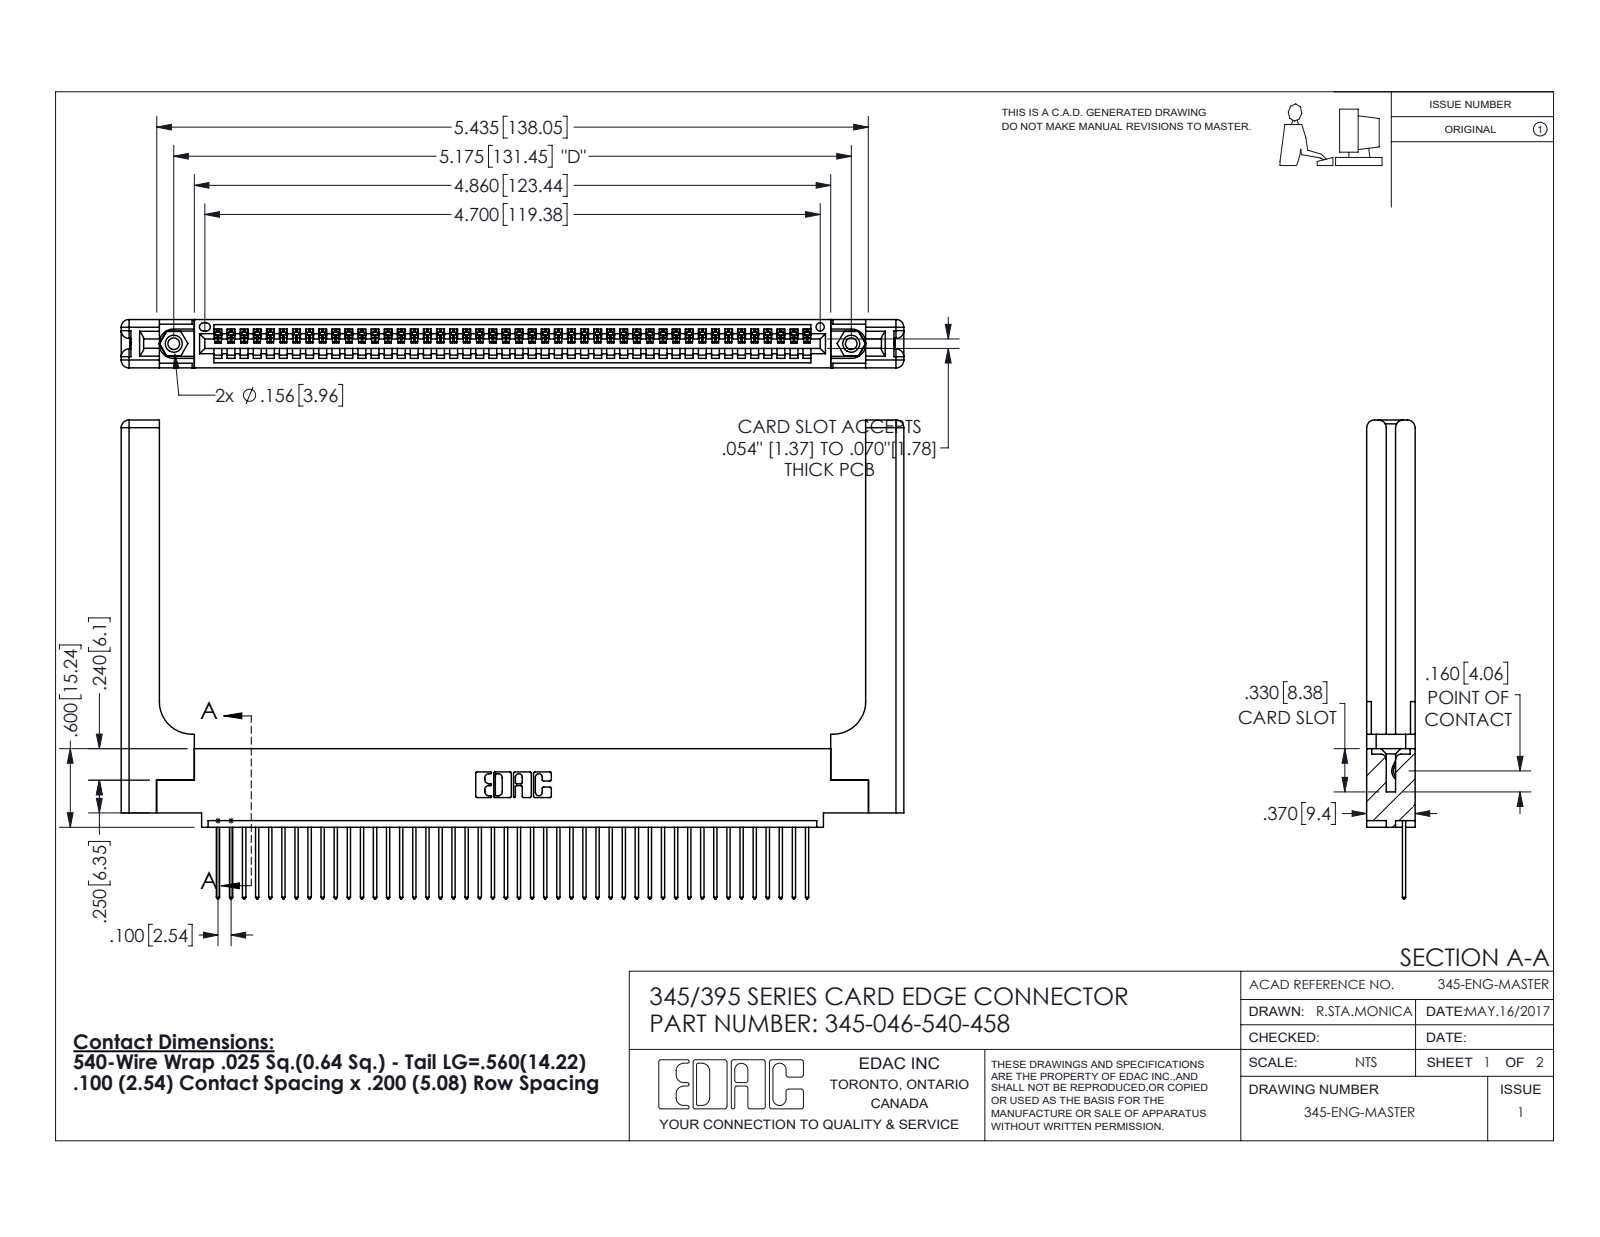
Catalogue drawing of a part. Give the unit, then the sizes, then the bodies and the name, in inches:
Units: inches
Overall size (bounding box): 5.979 × 3.657 × 0.37
Round holes (diameter × count): ⌀0.089 ×2, ⌀0.125 ×2, ⌀0.156 ×2, ⌀0.064 ×1
Round bosses / shafts (diameter × count): ⌀0.155 ×2
Partial cylindrical surfaces — rounded edges, fillets, slot ends (radius × count): R0.006 ×92, R0.01 ×92, R0.01 ×22, R0.06 ×16, R0.007 ×6, R0.031 ×6, R0.026 ×3, R0.03 ×2
Main face-to-face distances: 0.072, 0.37, 0.298, 0.098, 0.272, 0.025, 0.2, 0.225, 0.148, 0.15
Hole centre spacings: 0.27, 4.939, 5.175
Volume: 1.401 in³ · Surface area: 38.89 in²
Bodies: 51 solids, 3054 faces (2072 planar, 922 cylindrical, 60 other)
Part name (STEP PRODUCT): 345-046-540-458; 345 Part_0.110 Offset - 0.156 Dia-TH; 345-250-001_345-250-001-102; 345-292-001_345-293-140 (+1 more)
STEP written by: SolidWorks 2016 (CONFIG_CONTROL_DESIGN)
